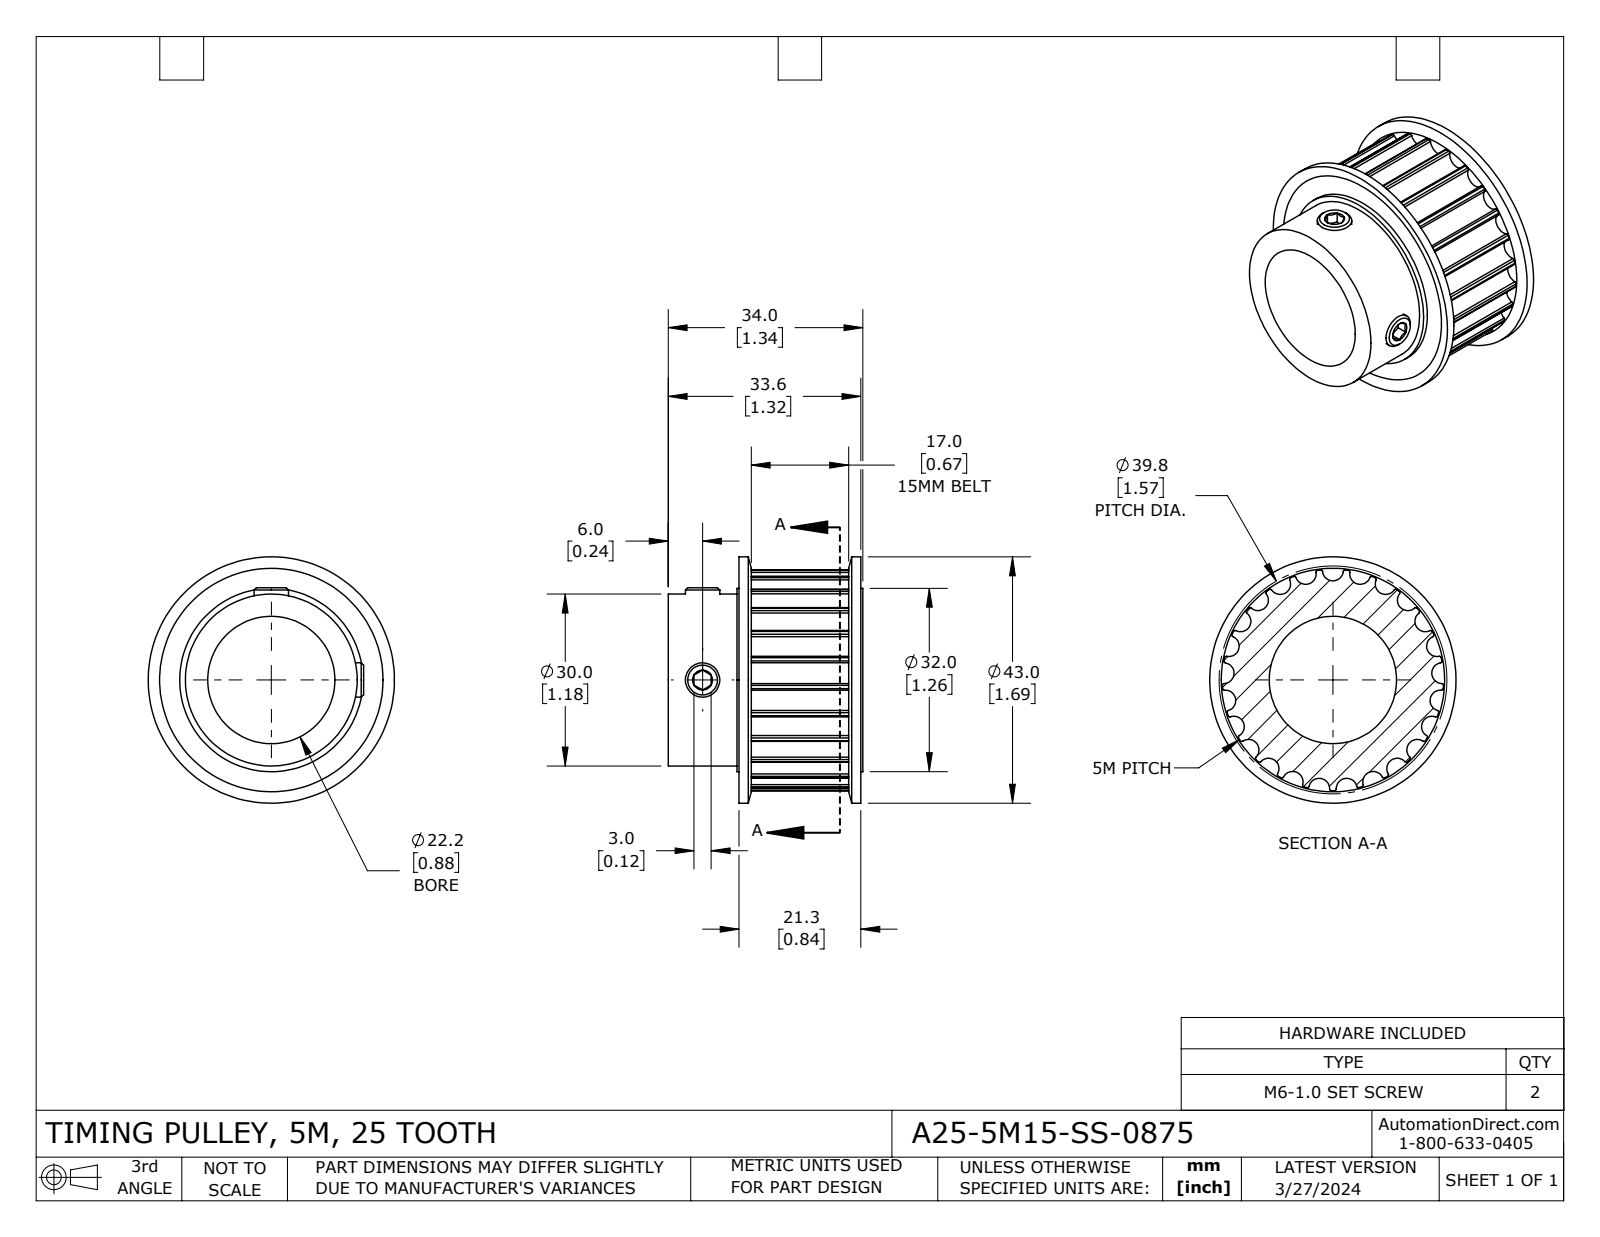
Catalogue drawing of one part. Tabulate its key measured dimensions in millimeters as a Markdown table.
| quantity | value |
| --- | --- |
| part name | A25-5M15-SS-0875 |
| STEP written by | SolidWorks 2021 (CONFIG_CONTROL_DESIGN) |
| units | millimeters |
| bodies | 5 solids, 208 faces (25 planar, 149 cylindrical, 34 other) |
| overall size | 43 × 43 × 34 |
| volume | 18 911 mm³ |
| surface area | 11 934 mm² |
| round holes (diameter × count) | 5 × 2, 22.23 × 1, 32 × 1 |
| round bosses / shafts (diameter × count) | 6 × 2, 43 × 1, 30 × 1 |
| partial cylindrical surfaces (radius × count) | 0.3 × 50, 1.82 × 25, 19.32 × 1 |
| main face-to-face distances | 1.6, 18.6, 17, 2.5, 19.5, 0.9, 21.1, 20.2, 34, 33.1 |
